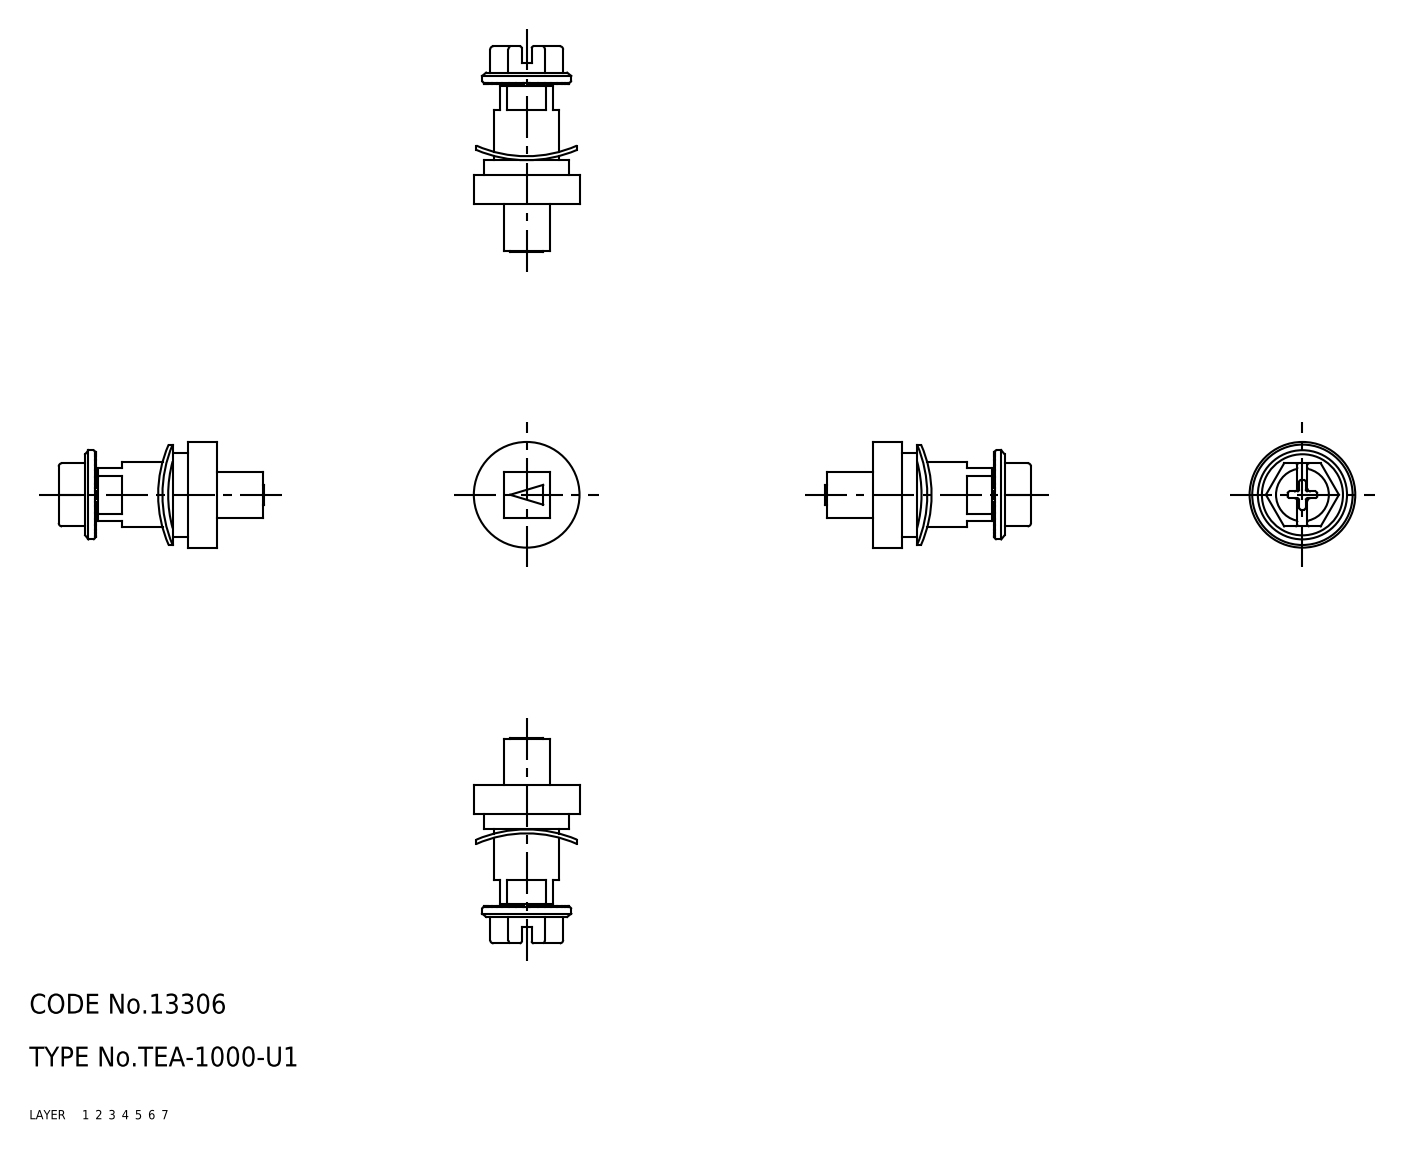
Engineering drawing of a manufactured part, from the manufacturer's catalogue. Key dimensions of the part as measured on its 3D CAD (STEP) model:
Part name (STEP PRODUCT): shaft
STEP written by: CADfix (AUTOMOTIVE_DESIGN)
Units: millimetres
Bodies: 1 solid, 140 faces (0 planar, 0 cylindrical, 140 other)
Overall size (bounding box): 31.15 × 16 × 16
Volume: 2 872 mm³ · Surface area: 1 973 mm²
